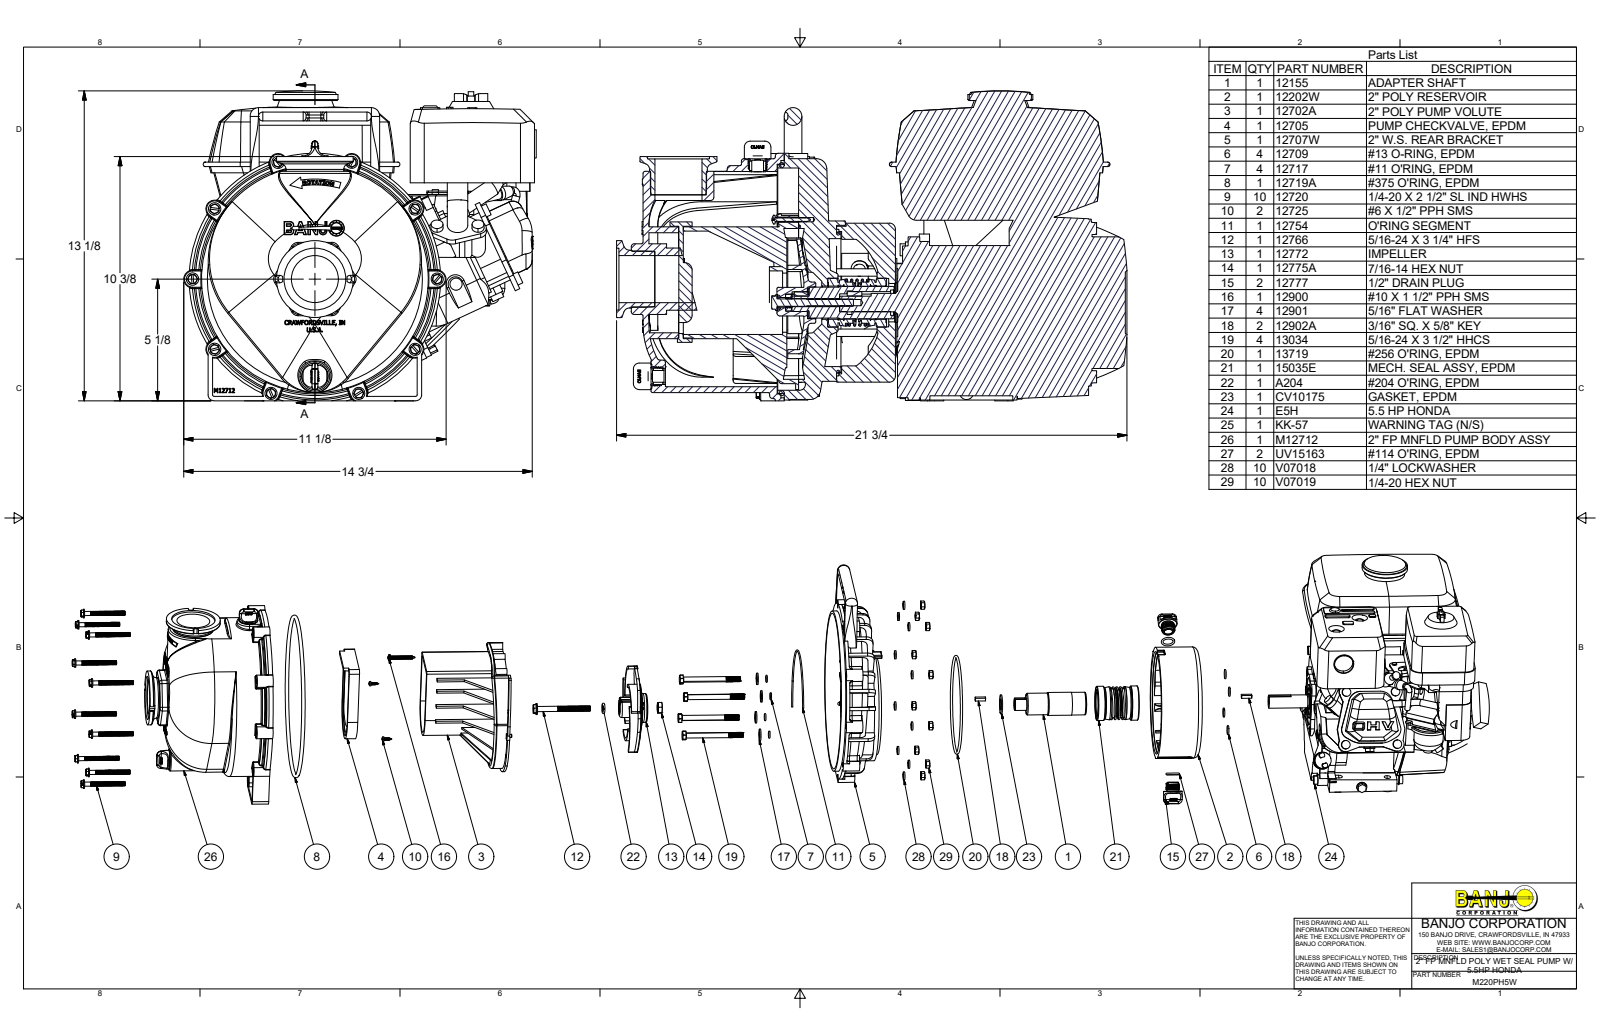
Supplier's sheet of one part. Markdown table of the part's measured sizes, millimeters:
| quantity | value |
| --- | --- |
| part name | M220PH5W; 12707W; 12707WX; 12703AWV (+8 more) |
| STEP written by | Autodesk Inventor 2017 (AUTOMOTIVE_DESIGN) |
| units | millimeters |
| bodies | 101 solids, 10139 faces (3179 planar, 2545 cylindrical, 4415 other) |
| overall size | 570.23 × 380.58 × 334.5 |
| volume | 19 690 000 mm³ |
| surface area | 1 997 000 mm² |
| round holes (diameter × count) | 4.98 × 10, 6.4 × 10, 6.86 × 10, 11.91 × 8, 5.59 × 7, 8.73 × 5, 7.95 × 4, 12.7 × 4, 14.25 × 4, 25.53 × 4, 2.87 × 2, 2.92 × 2 |
| round bosses / shafts (diameter × count) | 7.02 × 80, 13.21 × 10, 12.42 × 10, 6.35 × 10, 13 × 6, 4.88 × 6, 28.7 × 5, 7.94 × 5 |
| partial cylindrical surfaces (radius × count) | 0.76 × 141, 3.17 × 77, 0.38 × 50, 1.52 × 49, 4.76 × 34, 6.35 × 33, 0.2 × 26, 2 × 24 |
| main face-to-face distances | 4.57, 120, 73.15, 0.95, 4.13, 5.08, 40.36, 56.52, 63.48, 2.79 |
| hole center spacings | 78.4, 132.08, 17.52, 45.98, 63.5, 65.02, 89.8, 109.47 |
